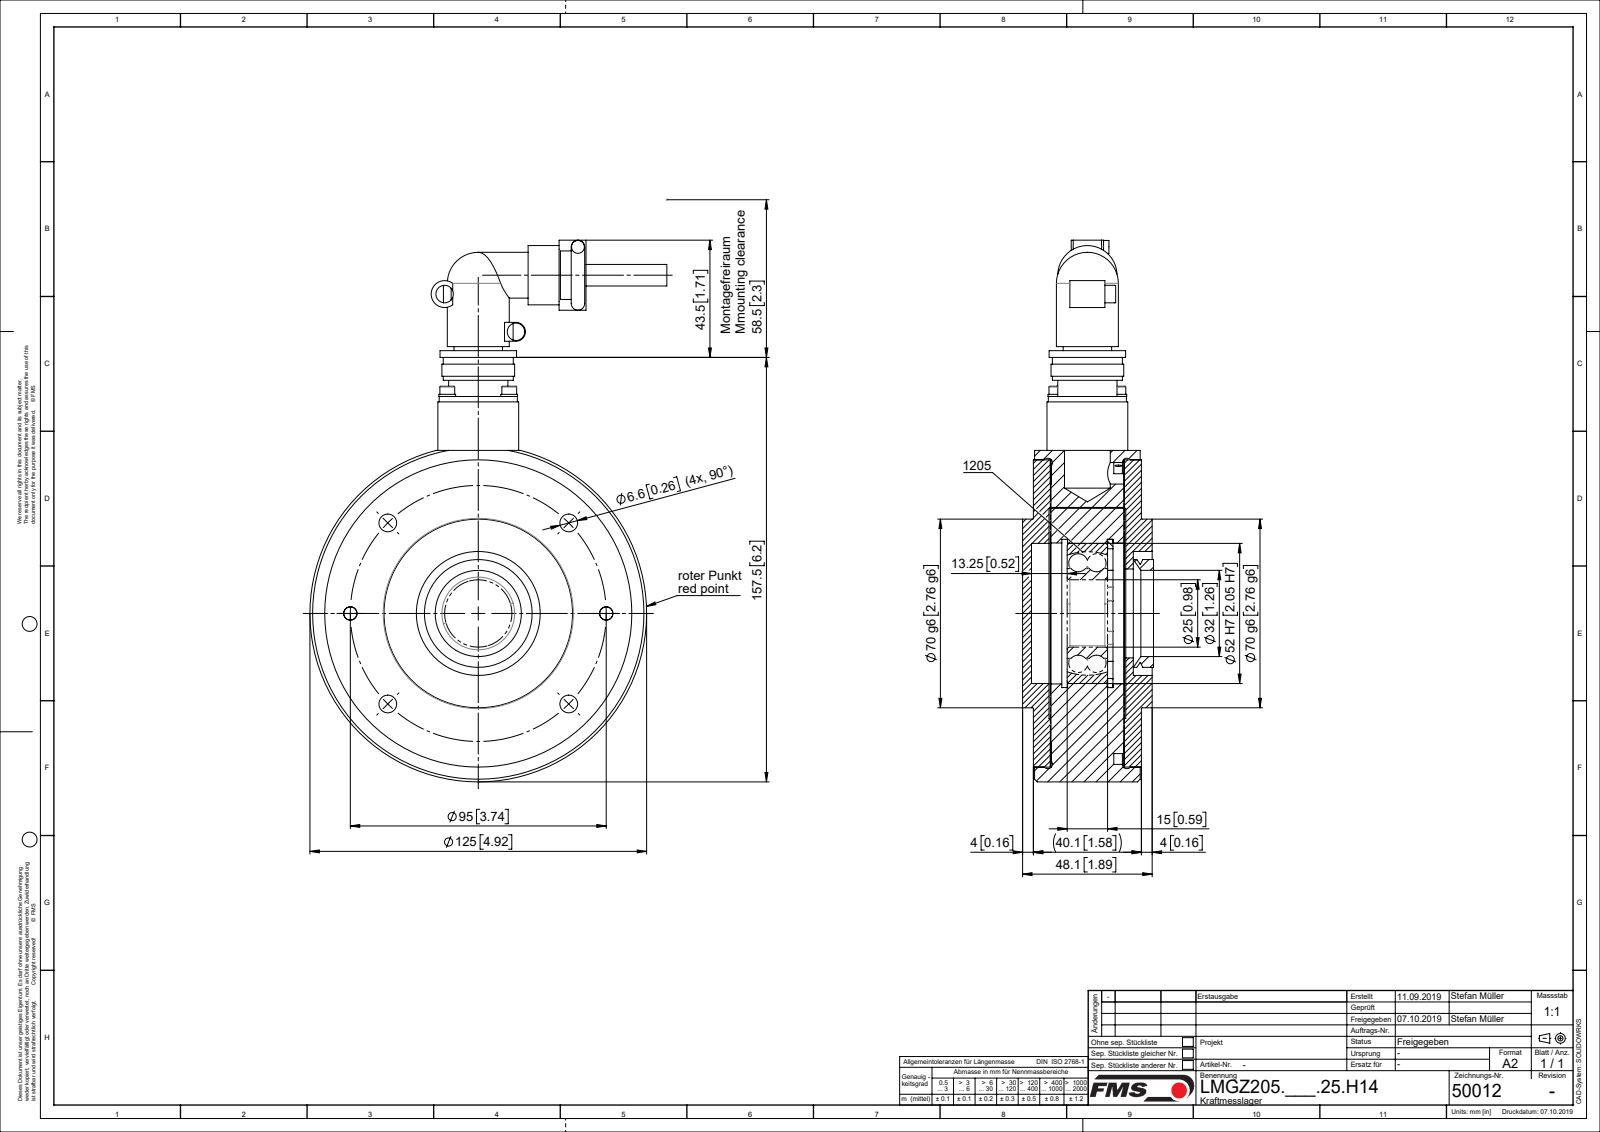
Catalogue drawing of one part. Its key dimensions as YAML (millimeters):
part_name: "L50012; L4832404; L47956; TEIL1 (+8 more)"
step_written_by: "Mechanical Desktop 2007 (CONFIG_CONTROL_DESIGN)"
units: millimeters
bodies: {solids: 20, faces: 412, planar: 119, cylindrical: 242, other: 51}
overall_size: [201, 132.5, 48.1]
volume: 490978
surface_area: 146421
round_holes:
  - {diameter: 6.6, count: 6}
  - {diameter: 2.6, count: 4}
  - {diameter: 3.2, count: 4}
  - {diameter: 3.4, count: 4}
  - {diameter: 3.5, count: 4}
  - {diameter: 5, count: 2}
  - {diameter: 11, count: 2}
  - {diameter: 23, count: 1}
  - {diameter: 25, count: 1}
  - {diameter: 31, count: 1}
  - {diameter: 33, count: 1}
  - {diameter: 37.9, count: 1}
round_bosses_or_shafts:
  - {diameter: 6.2, count: 4}
  - {diameter: 5.5, count: 4}
  - {diameter: 3, count: 4}
  - {diameter: 22, count: 2}
  - {diameter: 10, count: 2}
  - {diameter: 6.5, count: 2}
  - {diameter: 6, count: 2}
  - {diameter: 4.8, count: 2}
partial_cylinders:
  - {radius: 5, count: 9}
  - {radius: 2.5, count: 2}
  - {radius: 3.5, count: 1}
  - {radius: 40.5, count: 1}
  - {radius: 47, count: 1}
face_to_face_distances: [27.25, 33.55, 6.3, 6.55, 33.8, 27, 27.5, 4, 10.55, 37.8]
hole_center_spacings: [47.5, 16.26, 23, 36.36, 67.18, 87.77, 32.53, 95.01]
